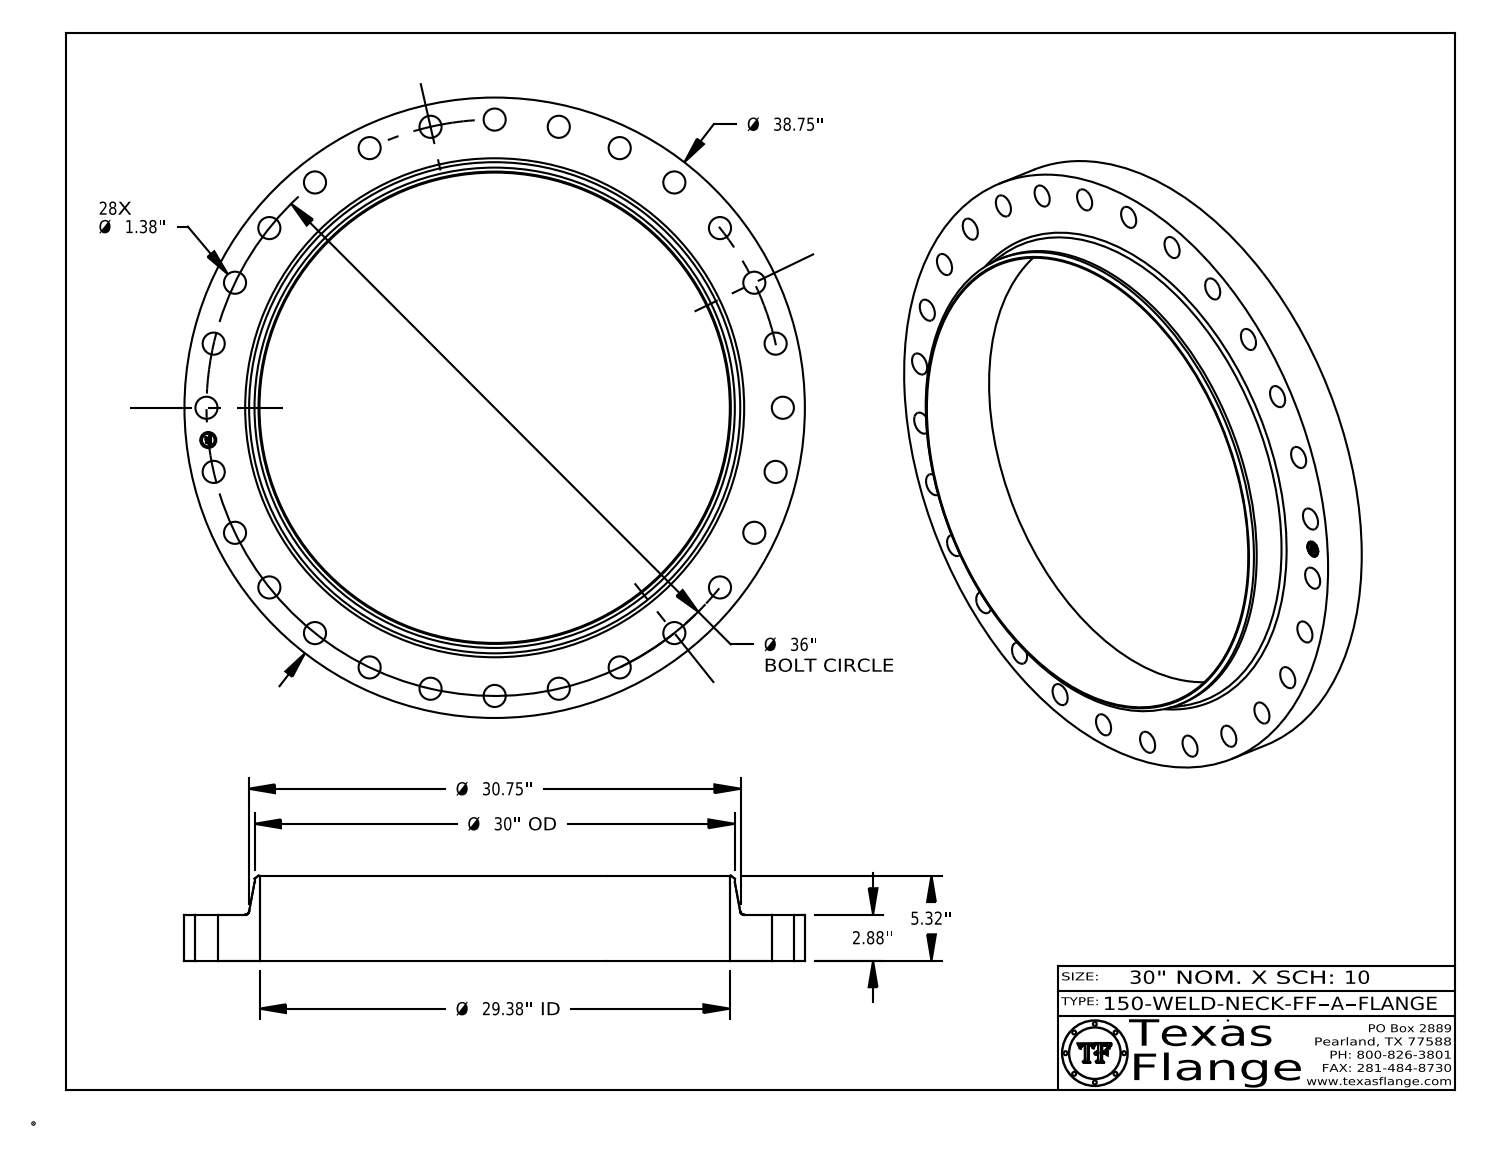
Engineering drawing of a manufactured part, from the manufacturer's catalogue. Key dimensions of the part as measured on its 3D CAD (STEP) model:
Part name (STEP PRODUCT): 150-WELD-NECK-FF, Series A
STEP written by: CATIA V5 STEP AP214 (AUTOMOTIVE_DESIGN)
Units: inches
Bodies: 1 solid, 456 faces (368 planar, 82 cylindrical, 6 other)
Overall size (bounding box): 38.75 × 38.75 × 5.32
Volume: 1 429 in³ · Surface area: 2 292 in²
Round holes (diameter × count): ⌀1.38 ×28, ⌀1 ×1, ⌀29.376 ×1
Round bosses / shafts (diameter × count): ⌀0.061 ×8, ⌀38.75 ×1, ⌀30 ×1, ⌀0.788 ×1
Main face-to-face distances: 2.88, 5.32, 2.44, 0.015, 2.865, 2.455, 0.298, 0.293, 0.054, 0.193
Hole centre spacings: 18, 19.153, 4.031, 8.011, 11.89, 15.62, 22.446, 25.456
